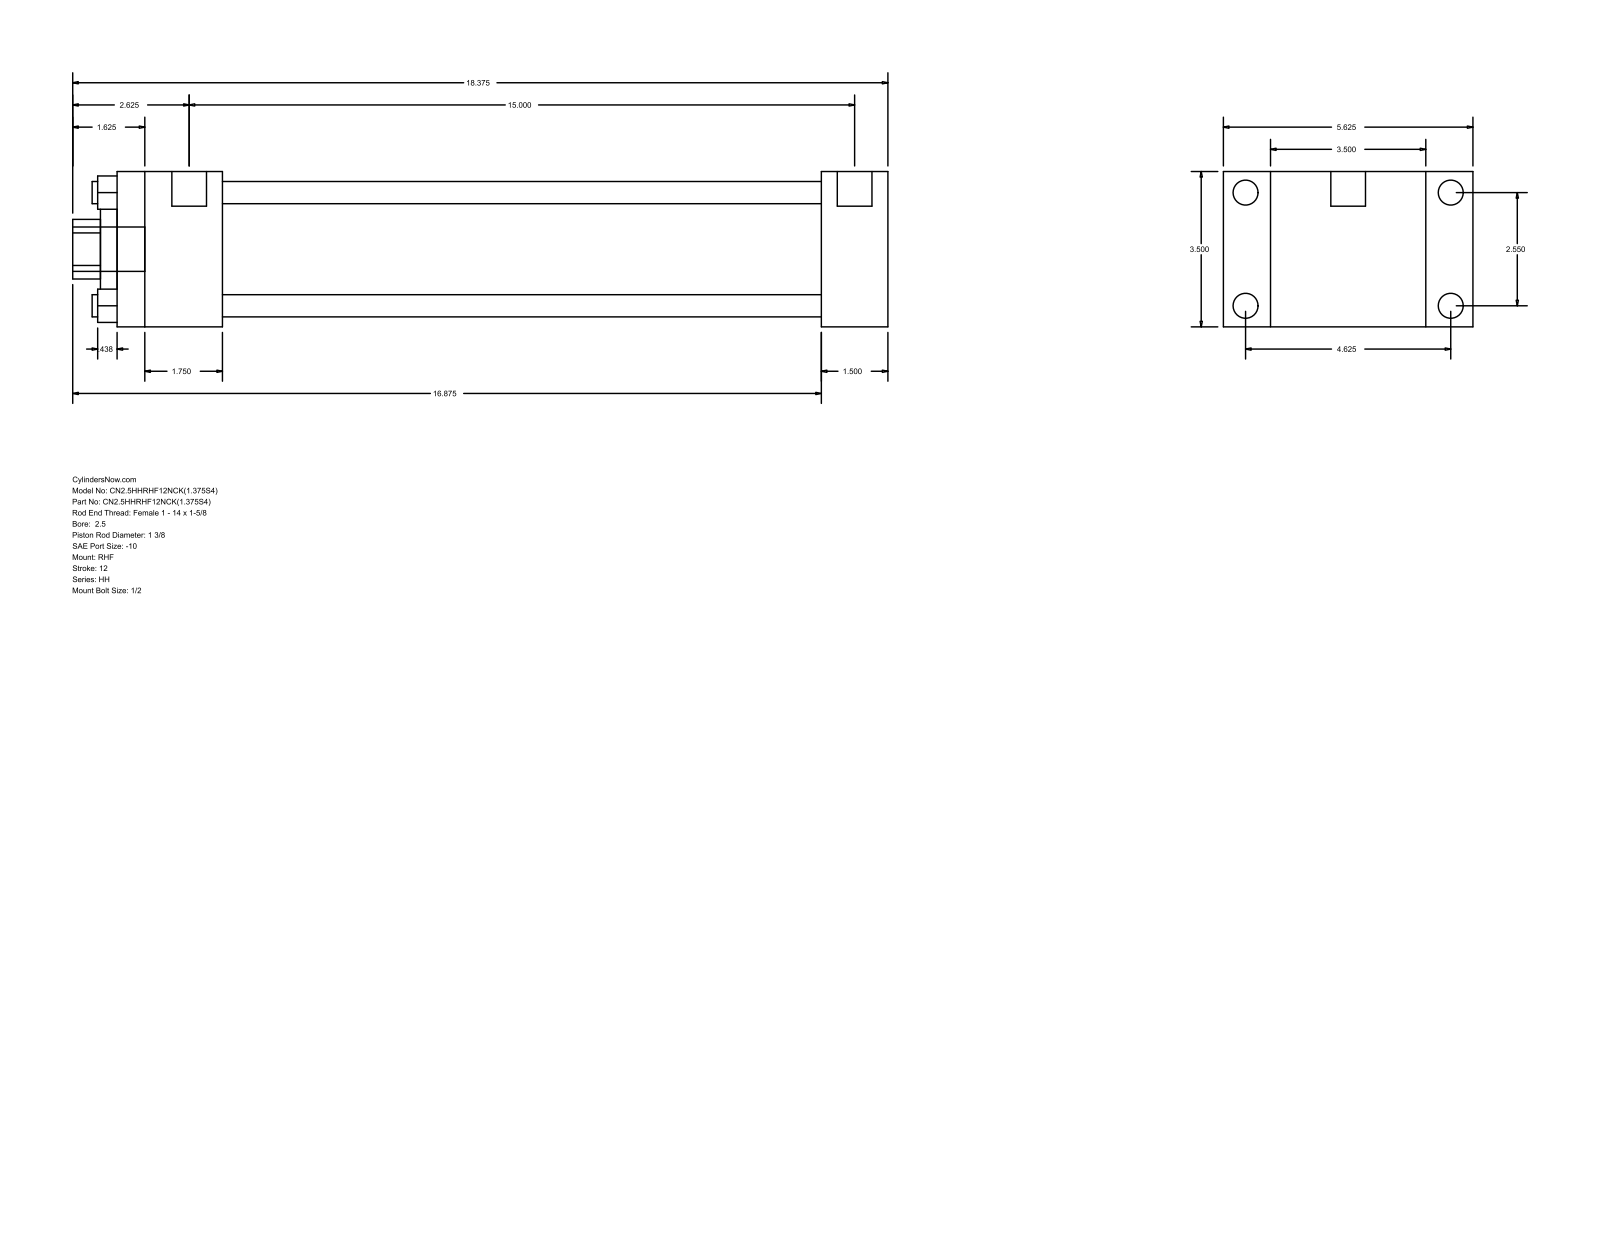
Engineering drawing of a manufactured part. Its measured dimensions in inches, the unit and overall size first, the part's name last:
Units: inches
Overall size (bounding box): 18.375 × 5.625 × 3.5
Round holes (diameter × count): ⌀0.5 ×4, ⌀1.375 ×1, ⌀2 ×1, ⌀2.875 ×1
Round bosses / shafts (diameter × count): ⌀0.563 ×4, ⌀0.219 ×4, ⌀0.781 ×2, ⌀1 ×1
Partial cylindrical surfaces — rounded edges, fillets, slot ends (radius × count): R0.672 ×1
Main face-to-face distances: 3.5, 1.5, 1.063, 4.563, 15.875, 17.375, 5.625, 2.375, 13.5, 15
Hole centre spacings: 1.803, 2.55, 3.606
Bodies: 0 solids, 88 faces (60 planar, 28 cylindrical, 0 other)
Part name (STEP PRODUCT): HH_RHF__0250_1.375
STEP written by: GSSL Pune (CONFIG_CONTROL_DESIGN)
